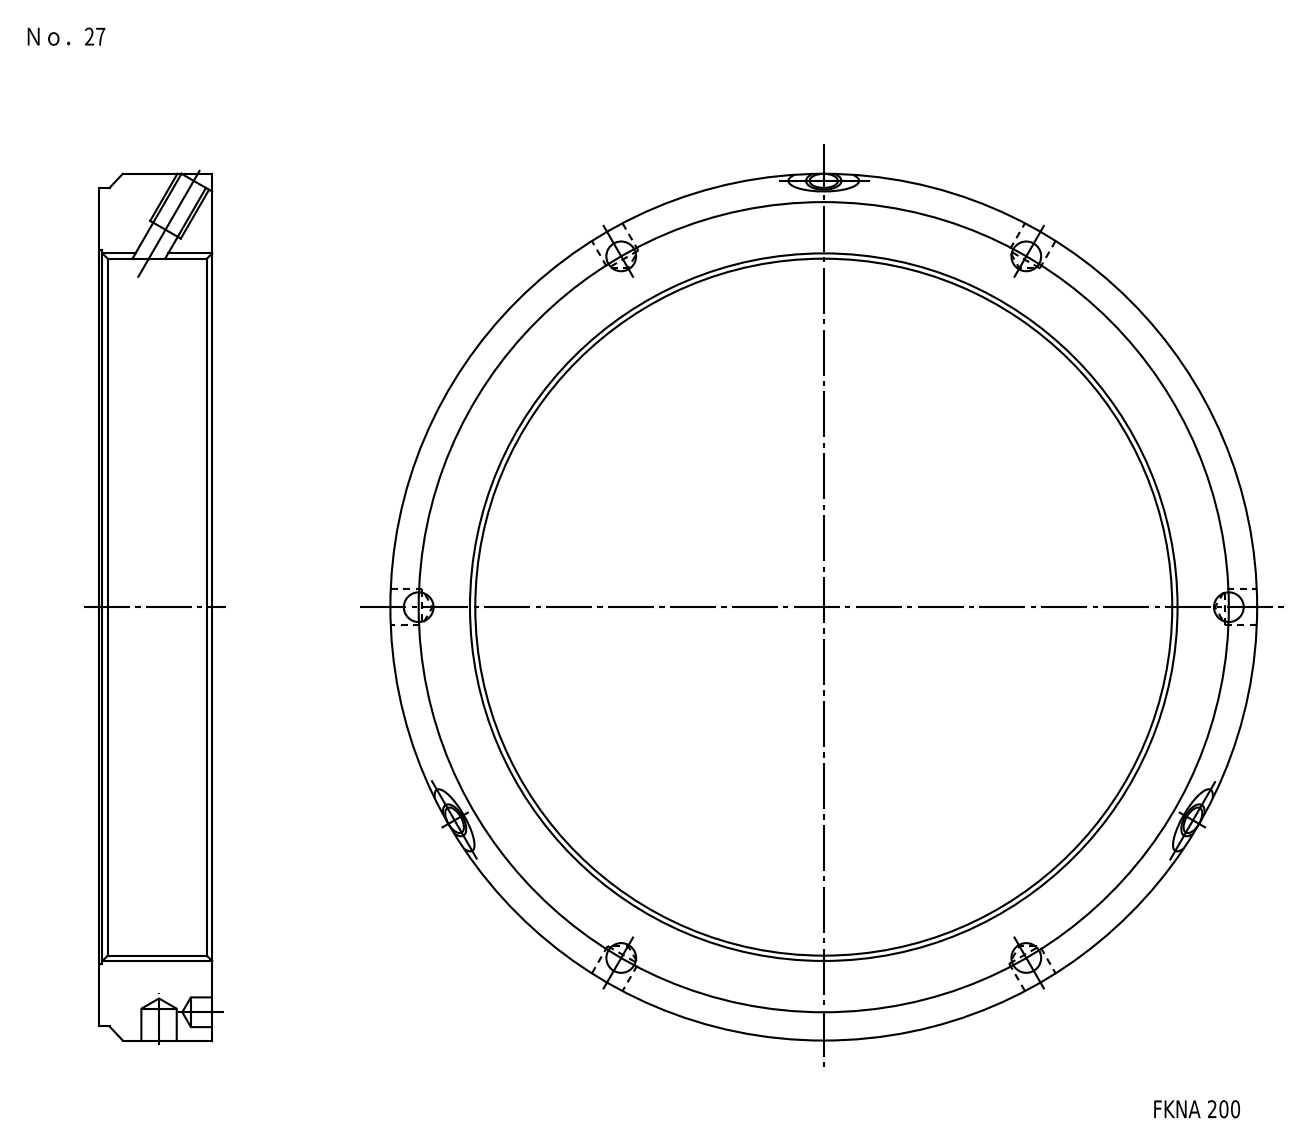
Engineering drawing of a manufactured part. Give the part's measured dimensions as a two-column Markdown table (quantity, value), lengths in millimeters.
| quantity | value |
| --- | --- |
| part name | FKD FKNA200 |
| STEP written by | Autodesk Inventor LT (CONFIG_CONTROL_DESIGN) |
| units | millimeters |
| bodies | 1 solid, 44 faces (6 planar, 25 cylindrical, 13 other) |
| overall size | 245 × 245 × 32 |
| volume | 483 786 mm³ |
| surface area | 78 900 mm² |
| round holes (diameter × count) | 8.4 × 6, 10 × 5, 8.38 × 3, 10.2 × 3, 200 × 1, 202 × 1 |
| round bosses / shafts (diameter × count) | 245 × 1, 237 × 1 |
| partial cylindrical surfaces (radius × count) | 20 × 3 |
| main face-to-face distances | 32, 1.5, 30.5 |
| hole center spacings | 114.5, 198.32, 229 |
